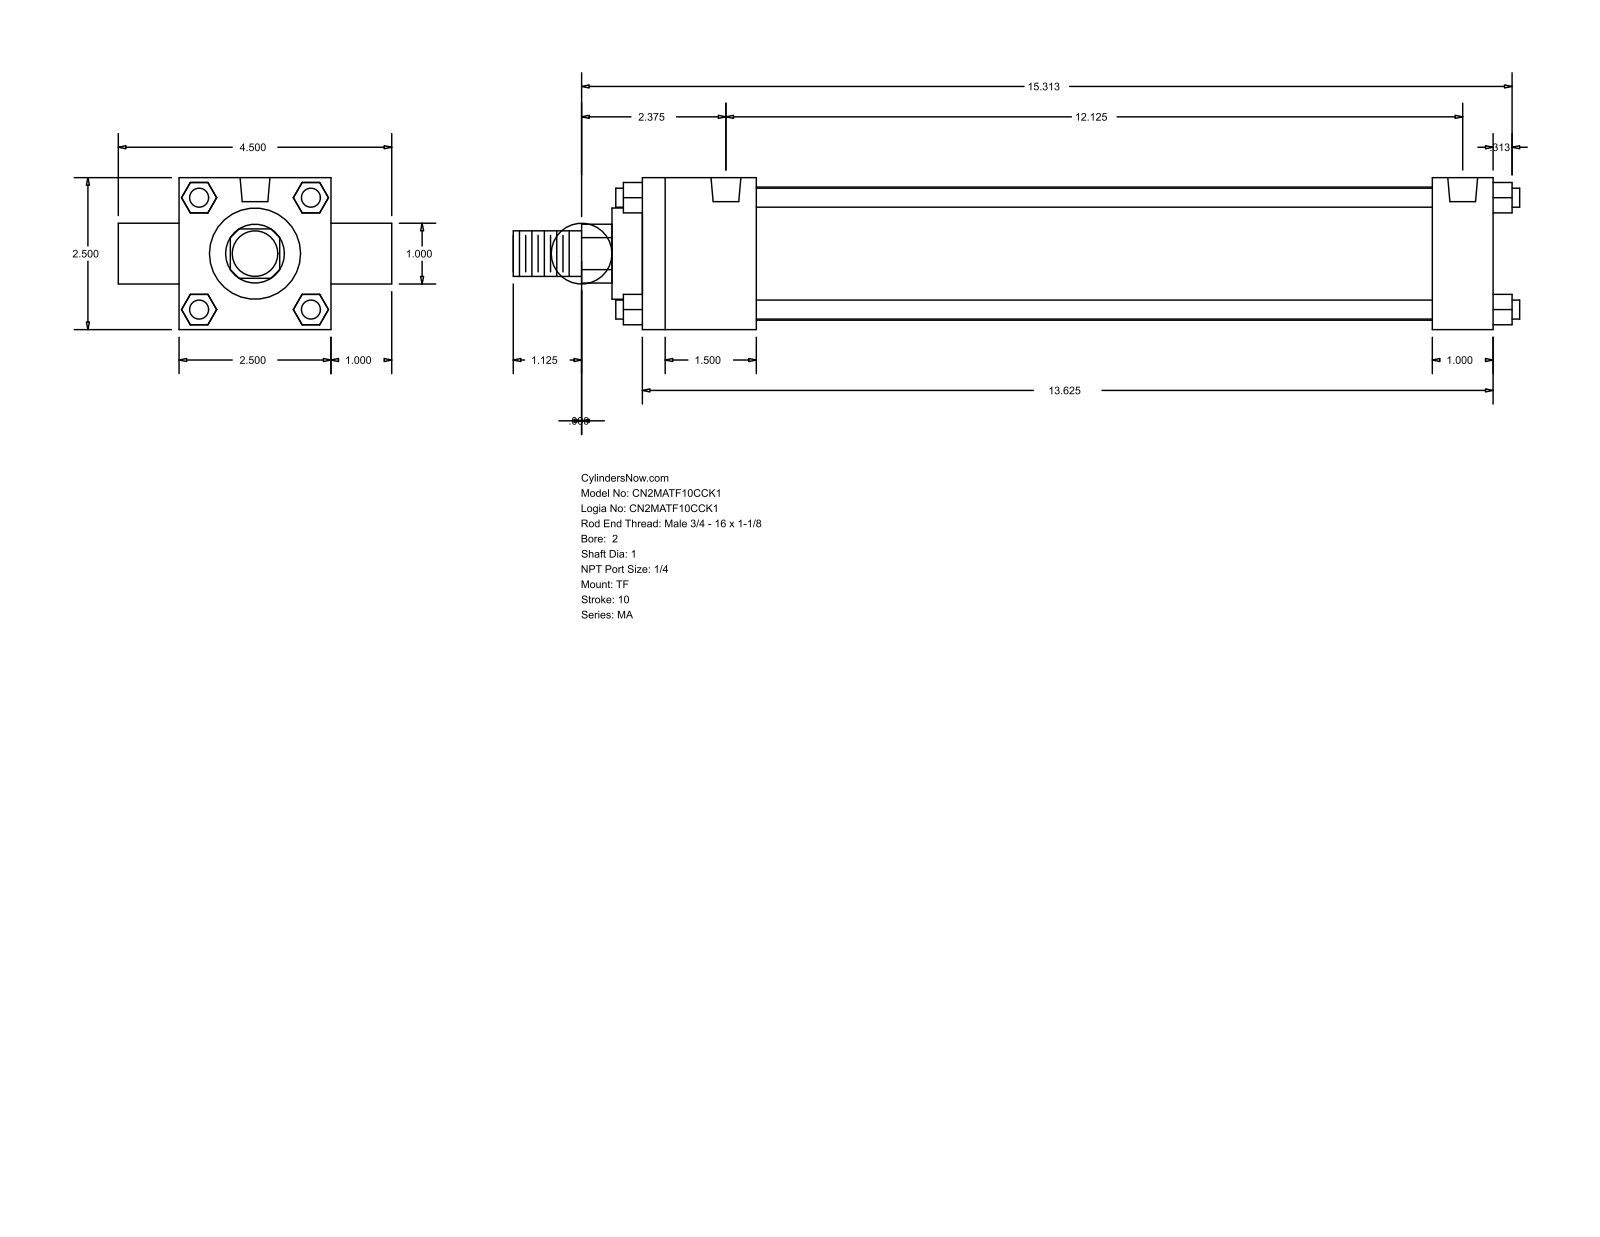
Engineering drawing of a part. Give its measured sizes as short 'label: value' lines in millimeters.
name: MA_TF__0200_1
written by: GSSL Pune (CONFIG_CONTROL_DESIGN)
unit: mm
bodies: 0 solids, 120 faces (92 planar, 28 cylindrical, 0 other)
size: 420.69 × 114.3 × 63.5
holes: 3× ⌀7.94, 2× ⌀12.49
bosses: 4× ⌀7.94, 2× ⌀25.4, 1× ⌀55.63, 1× ⌀38.1, 1× ⌀19.05
rounds: 1× R12.29
face distances: 63.5, 25.4, 355.6, 12.7, 47.63, 330.2, 282.57, 307.97, 88.9, 40.47
hole spacings: 307.97
